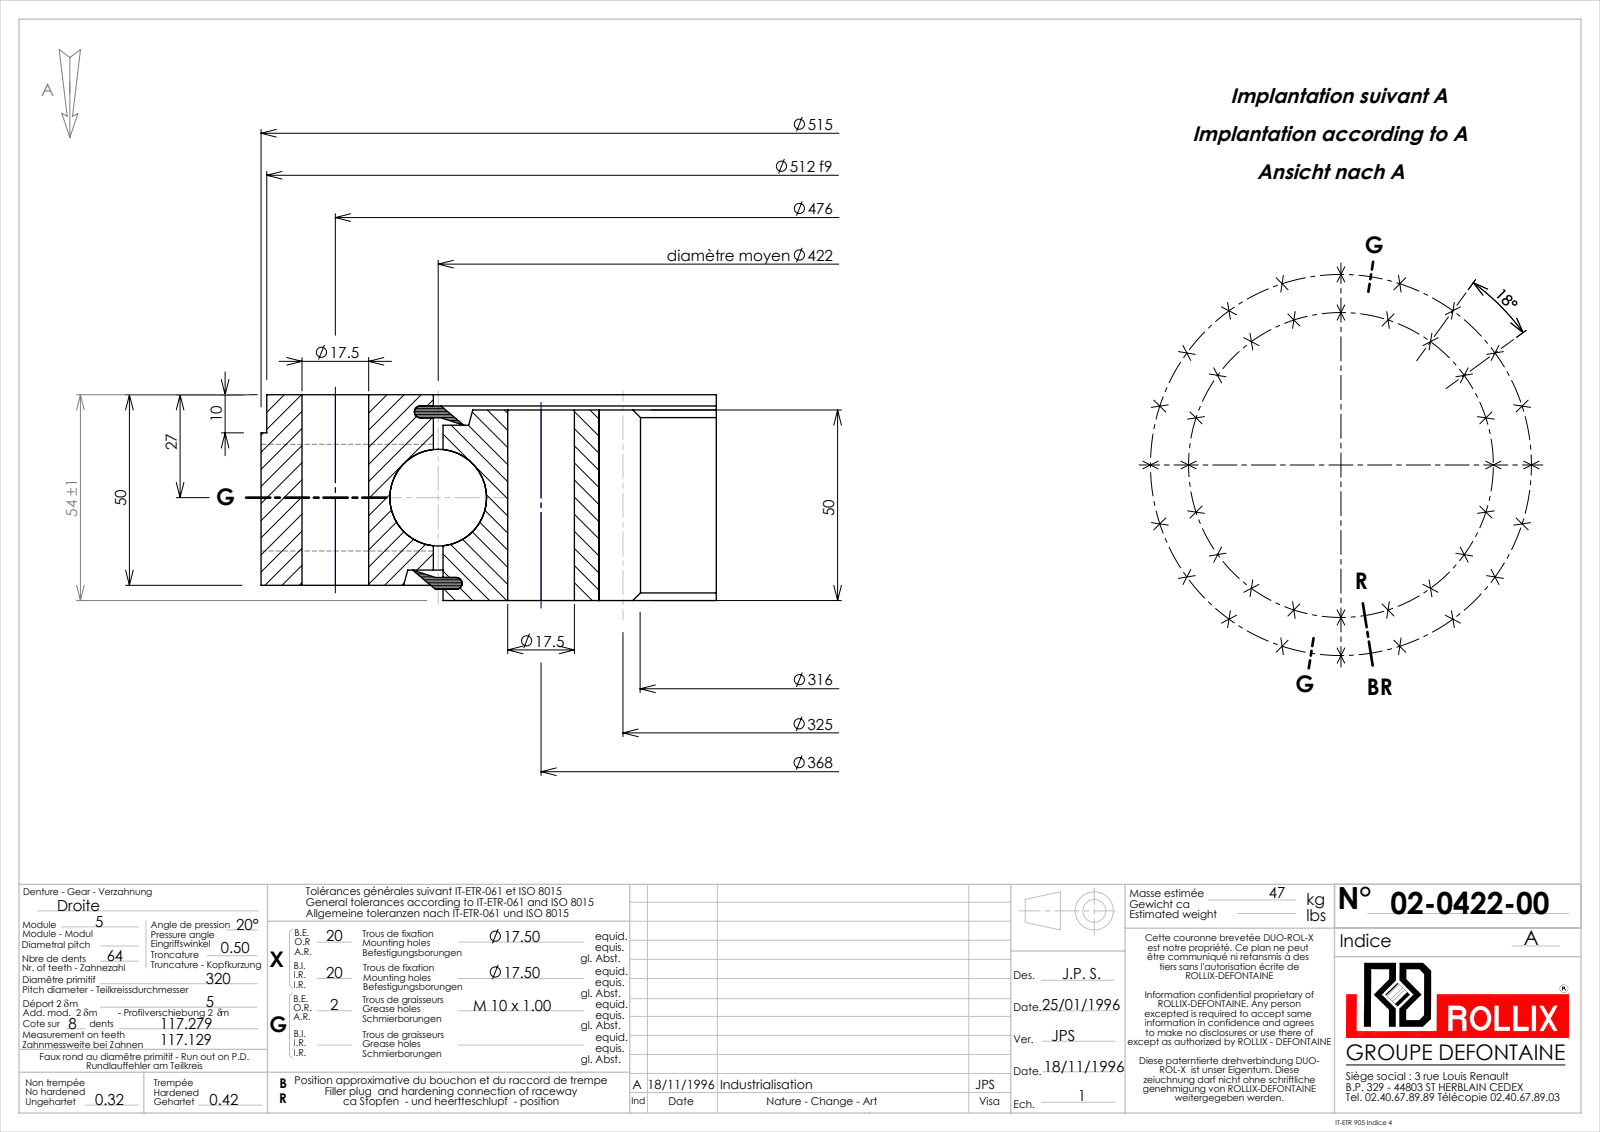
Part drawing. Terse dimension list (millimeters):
name: 02-0422-00
written by: SolidWorks 2016 (CONFIG_CONTROL_DESIGN)
unit: mm
bodies: 5 solids, 536 faces (143 planar, 229 cylindrical, 164 other)
size: 515 × 515 × 54
volume: 4 949 000 mm³; area: 779 772 mm²
holes: 40× ⌀17.5, 2× ⌀9, 1× ⌀424.54
bosses: 1× ⌀515, 1× ⌀512, 1× ⌀419.46
rounds: 1× R158, 1× R168.75
face distances: 4, 50, 46, 54, 6.05, 47.95, 2.05, 43.95, 2.95, 51.05
hole spacings: 113.72, 300.83, 327.89, 363.47, 376.8, 416.89, 167.07, 260.21
